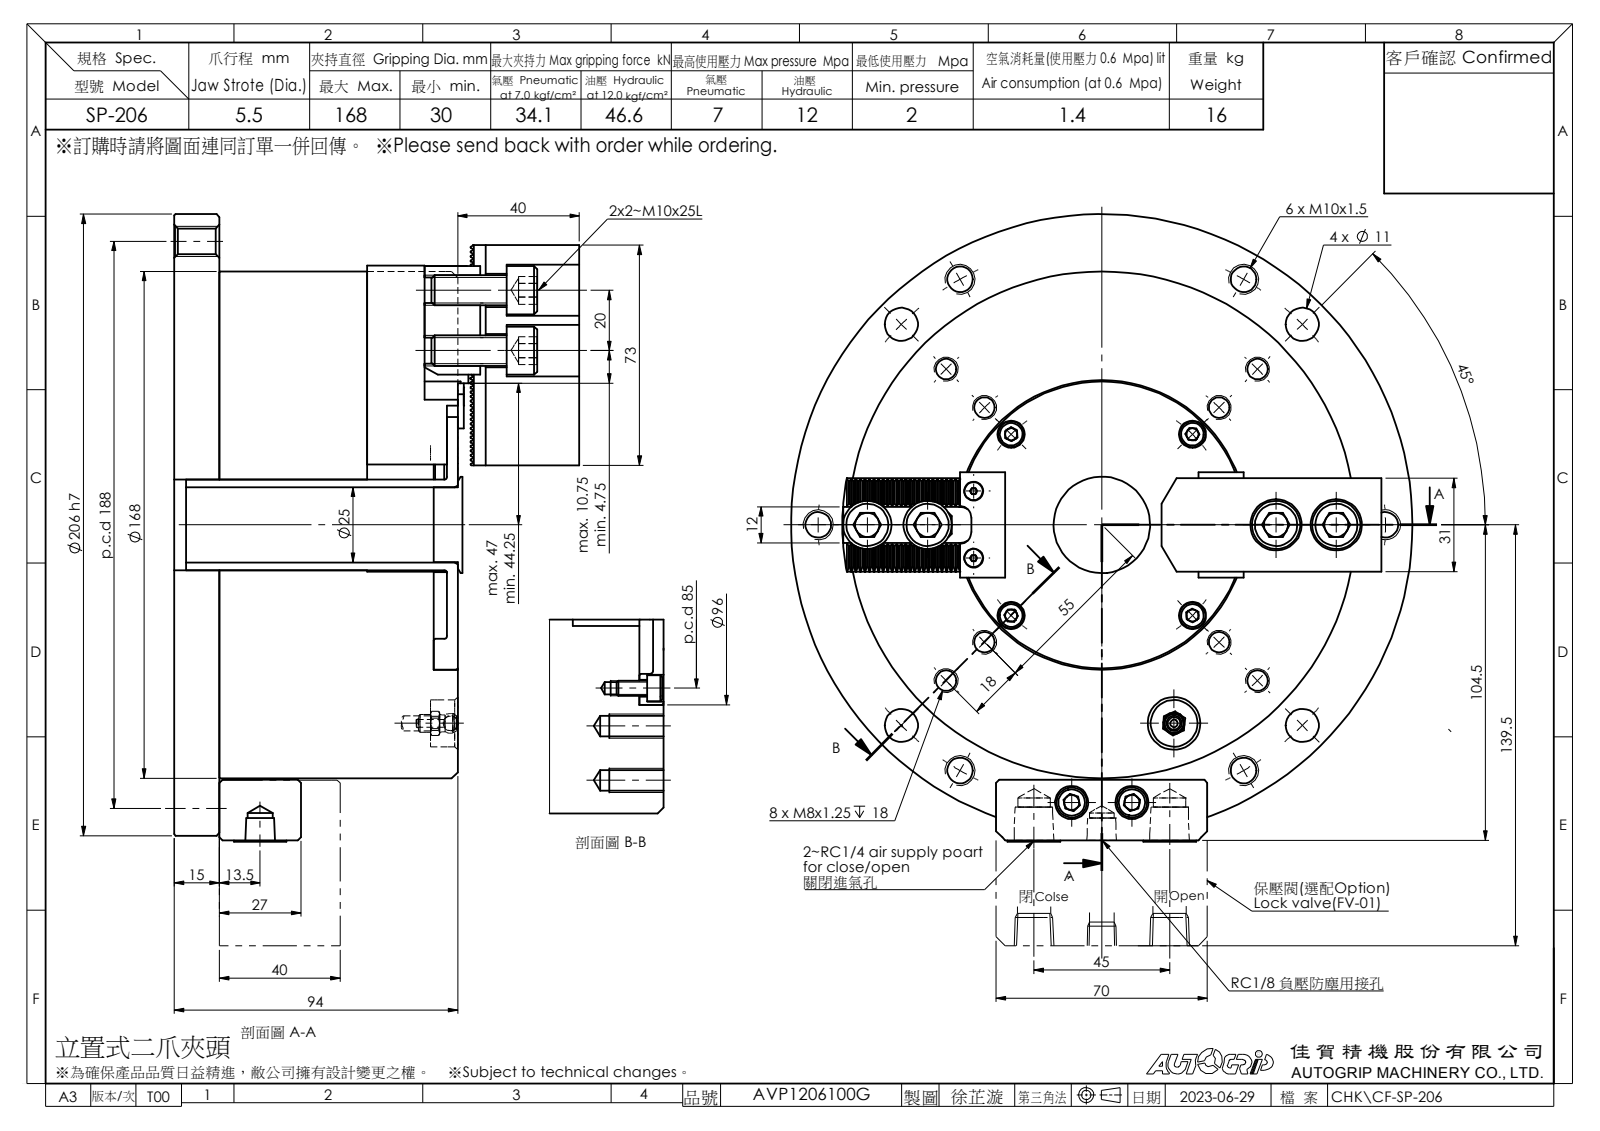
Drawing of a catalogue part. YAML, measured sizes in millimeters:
part_name: "CF-SP-306-06010; 錐平頭六角孔螺栓_M3x6; CF-SP-206-01000; CF-SU-308-07000 (+8 more)"
step_written_by: "SolidWorks 2020 (CONFIG_CONTROL_DESIGN)"
units: millimeters
bodies: {solids: 32, faces: 2086, planar: 1339, cylindrical: 522, other: 225}
overall_size: [208, 206, 134.3]
volume: 2347000
surface_area: 301987
round_holes:
  - {diameter: 8.5, count: 10}
  - {diameter: 11, count: 10}
  - {diameter: 6.8, count: 8}
  - {diameter: 3.4, count: 4}
  - {diameter: 4.1, count: 4}
  - {diameter: 5, count: 4}
  - {diameter: 5.5, count: 4}
  - {diameter: 9, count: 4}
  - {diameter: 17, count: 4}
  - {diameter: 6.6, count: 2}
  - {diameter: 10.5, count: 2}
  - {diameter: 10.7, count: 2}
round_bosses_or_shafts:
  - {diameter: 6, count: 7}
  - {diameter: 10, count: 6}
  - {diameter: 3, count: 5}
  - {diameter: 16, count: 4}
  - {diameter: 8.5, count: 4}
  - {diameter: 5, count: 4}
  - {diameter: 17.5, count: 2}
  - {diameter: 11.5, count: 2}
partial_cylinders:
  - {radius: 0.2, count: 98}
  - {radius: 0.1, count: 50}
  - {radius: 4, count: 4}
  - {radius: 6, count: 2}
  - {radius: 82.5, count: 2}
  - {radius: 37.75, count: 1}
  - {radius: 48, count: 1}
face_to_face_distances: [15, 94, 79, 31, 64, 30, 49, 22, 8, 90.5]
hole_center_spacings: [94, 69.5, 84.47, 91.4, 103.16, 108.91, 119.02, 12.5]
